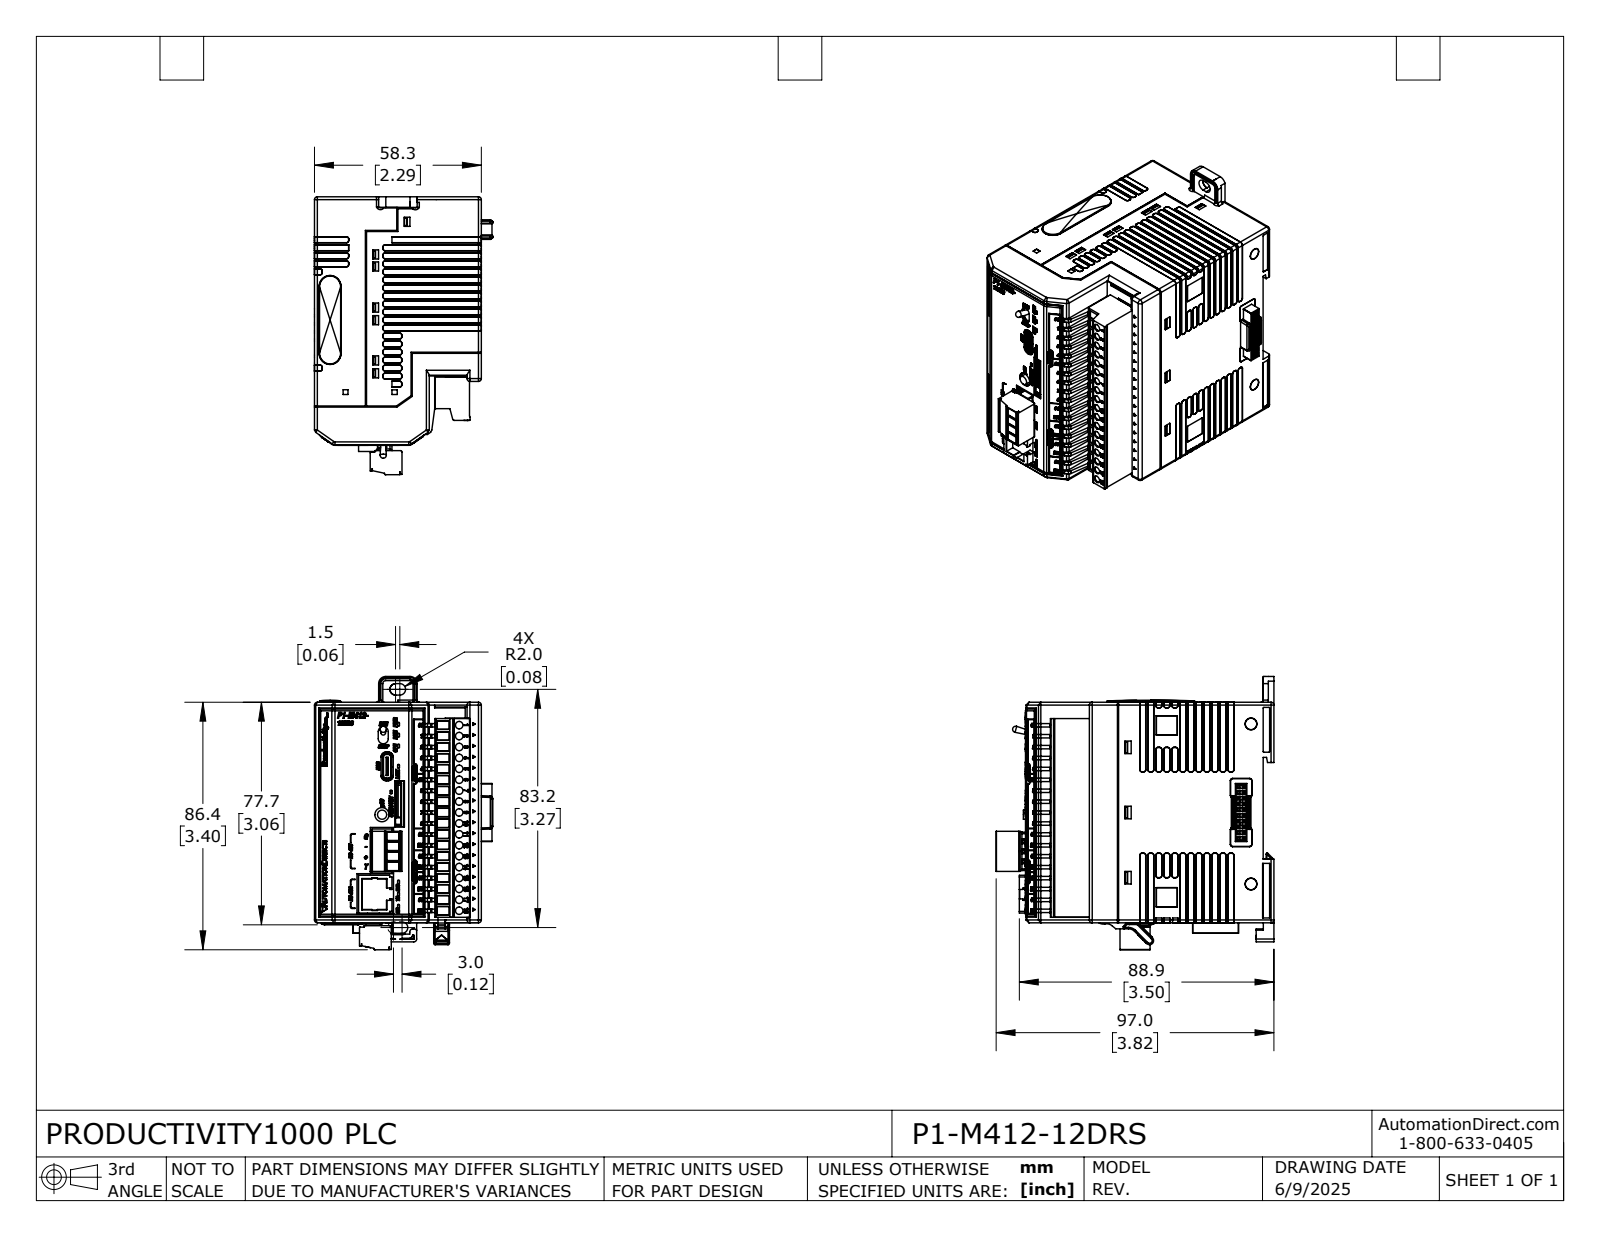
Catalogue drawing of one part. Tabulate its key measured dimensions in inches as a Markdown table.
| quantity | value |
| --- | --- |
| part name | P1-M412-12DRS |
| STEP written by | SolidWorks 2024 (AUTOMOTIVE_DESIGN) |
| units | inches |
| bodies | 24 solids, 3661 faces (2093 planar, 895 cylindrical, 673 other) |
| overall size | 3.686 × 3.593 × 2.452 |
| volume | 2.099 in³ |
| surface area | 105 in² |
| round holes (diameter × count) | 0.194 × 1 |
| round bosses / shafts (diameter × count) | 0.214 × 1, 0.126 × 1 |
| partial cylindrical surfaces (radius × count) | 0.01 × 172, 0.008 × 86, 0.02 × 49, 0.039 × 33, 0.079 × 8, 0.024 × 7, 0.004 × 6, 0.012 × 4 |
| main face-to-face distances | 2.235, 0.02, 0.039, 2.275, 3.01, 3.022, 2.294, 2.294, 2.255, 3.02 |
